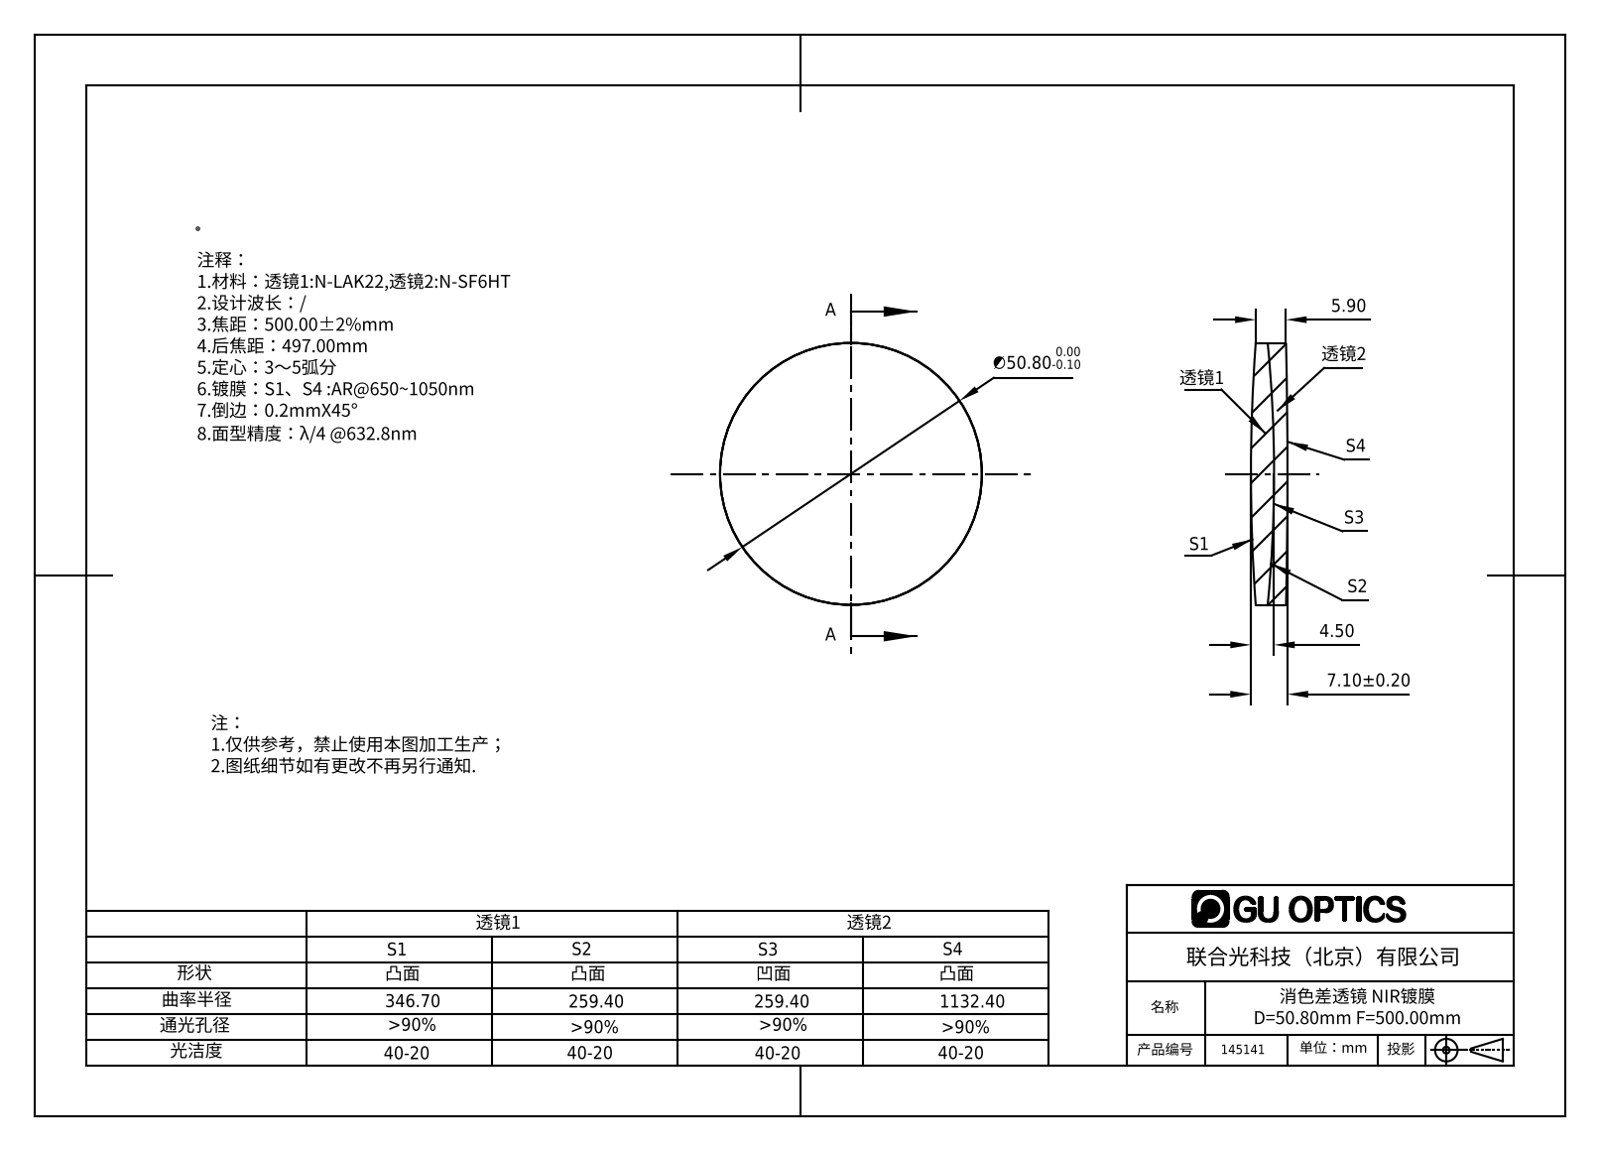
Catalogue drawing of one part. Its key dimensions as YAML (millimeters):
part_name: "145141"
step_written_by: "SolidWorks 2016 (AUTOMOTIVE_DESIGN)"
units: millimeters
bodies: {solids: 2, faces: 12, planar: 0, cylindrical: 4, other: 8}
overall_size: [50.8, 50.8, 7.1]
volume: 13158
surface_area: 9059
round_bosses_or_shafts:
  - {diameter: 50.8, count: 1}
